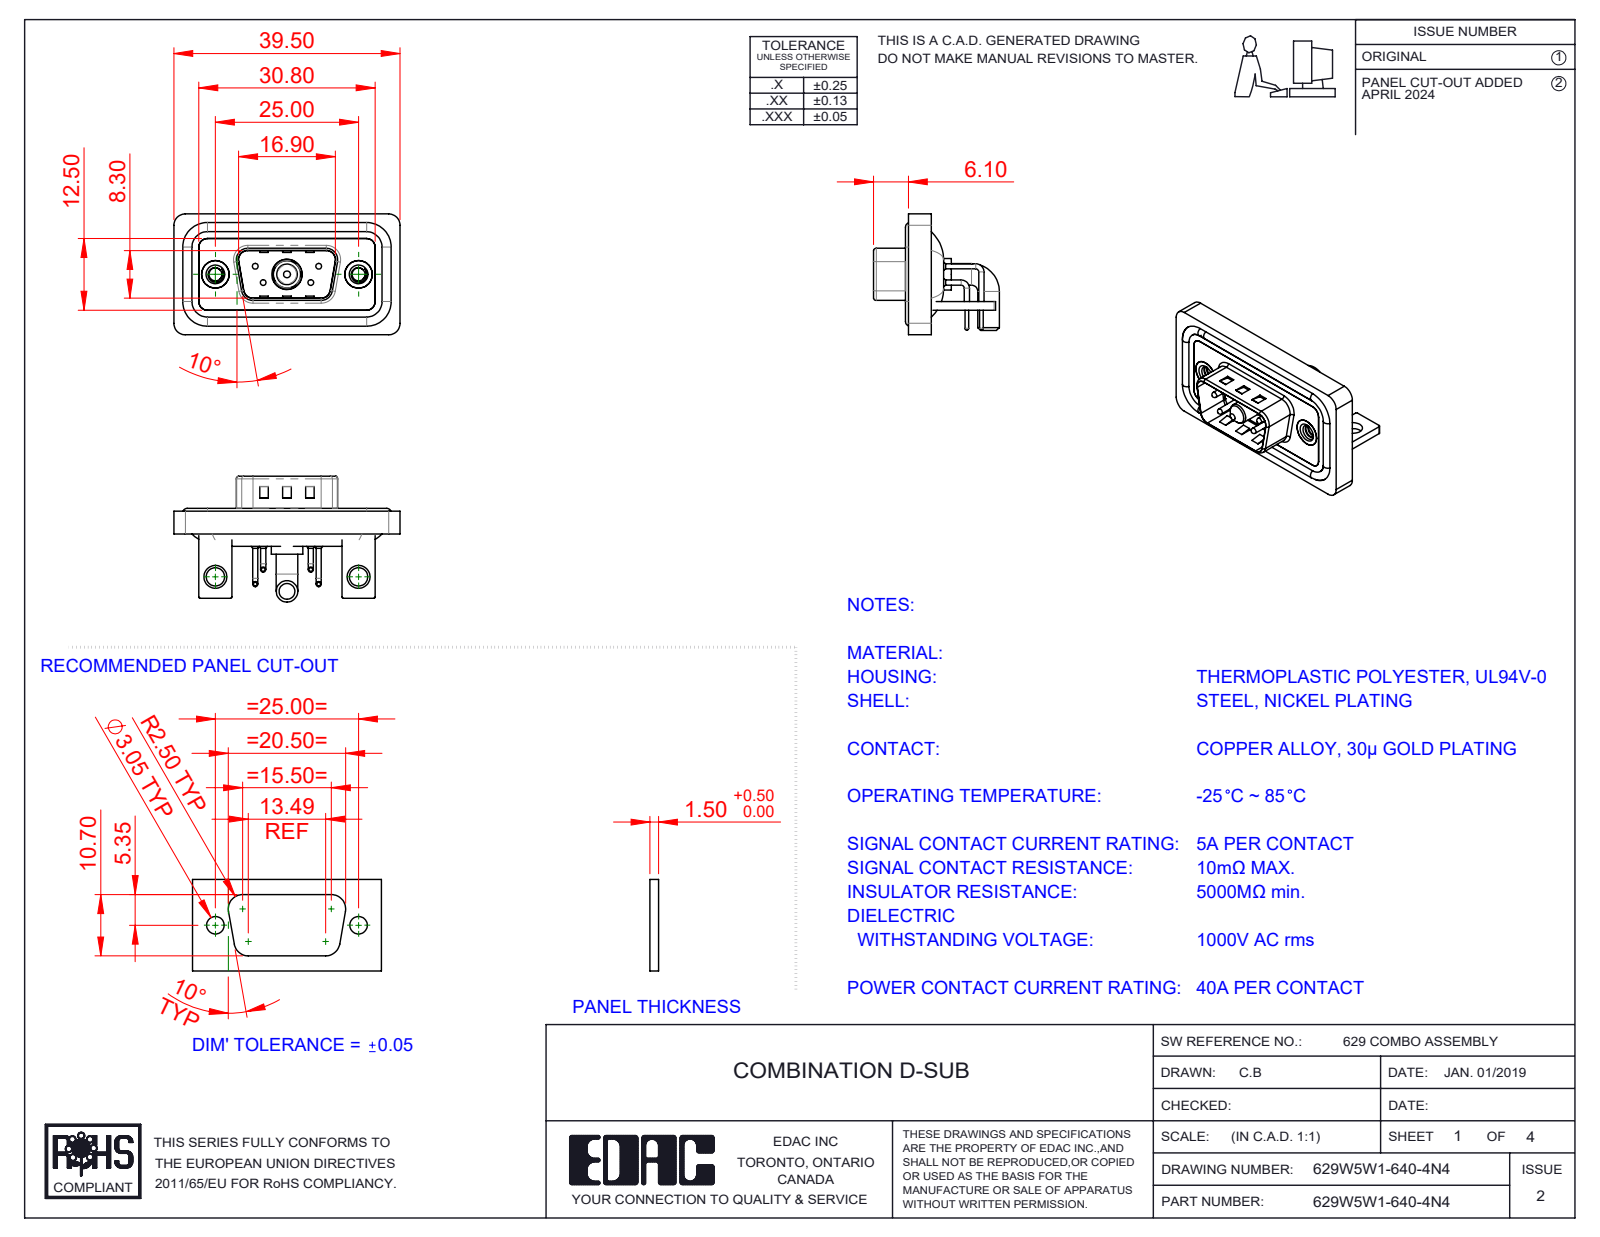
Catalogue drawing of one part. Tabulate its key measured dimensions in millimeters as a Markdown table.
| quantity | value |
| --- | --- |
| part name | 629Combo Stabilizer Bracket; 629Combo Contact Row 1; 629Combo Housing_5W1; 629Combo Shell Front_09 Contacts (+6 more) |
| STEP written by | SolidWorks 2023 (CONFIG_CONTROL_DESIGN) |
| units | millimeters |
| bodies | 15 solids, 934 faces (431 planar, 363 cylindrical, 140 other) |
| overall size | 39.5 × 21.98 × 21.1 |
| volume | 4 826 mm³ |
| surface area | 7 794 mm² |
| round holes (diameter × count) | 0.75 × 4, 1.6 × 4, 2 × 4, 2.26 × 2, 3.2 × 2, 4 × 2, 4.8 × 2, 5 × 2, 4.85 × 1, 5.3 × 1 |
| round bosses / shafts (diameter × count) | 0.9 × 8, 1.6 × 4, 1.5 × 4, 1 × 4, 0.65 × 4, 4.9 × 2, 3.75 × 2, 5.5 × 1 |
| partial cylindrical surfaces (radius × count) | 2 × 19, 1.5 × 18, 0.25 × 16, 0.5 × 9, 1.6 × 8, 0.6 × 4, 0.65 × 4, 0.9 × 4 |
| main face-to-face distances | 0.4, 1.5, 0.8, 2.9, 1.1, 2.1, 1.2, 1.6, 2.5, 3.7 |
| hole center spacings | 3.16, 5.72, 7.1, 12.5, 18.1, 25, 4.39, 4.4 |
